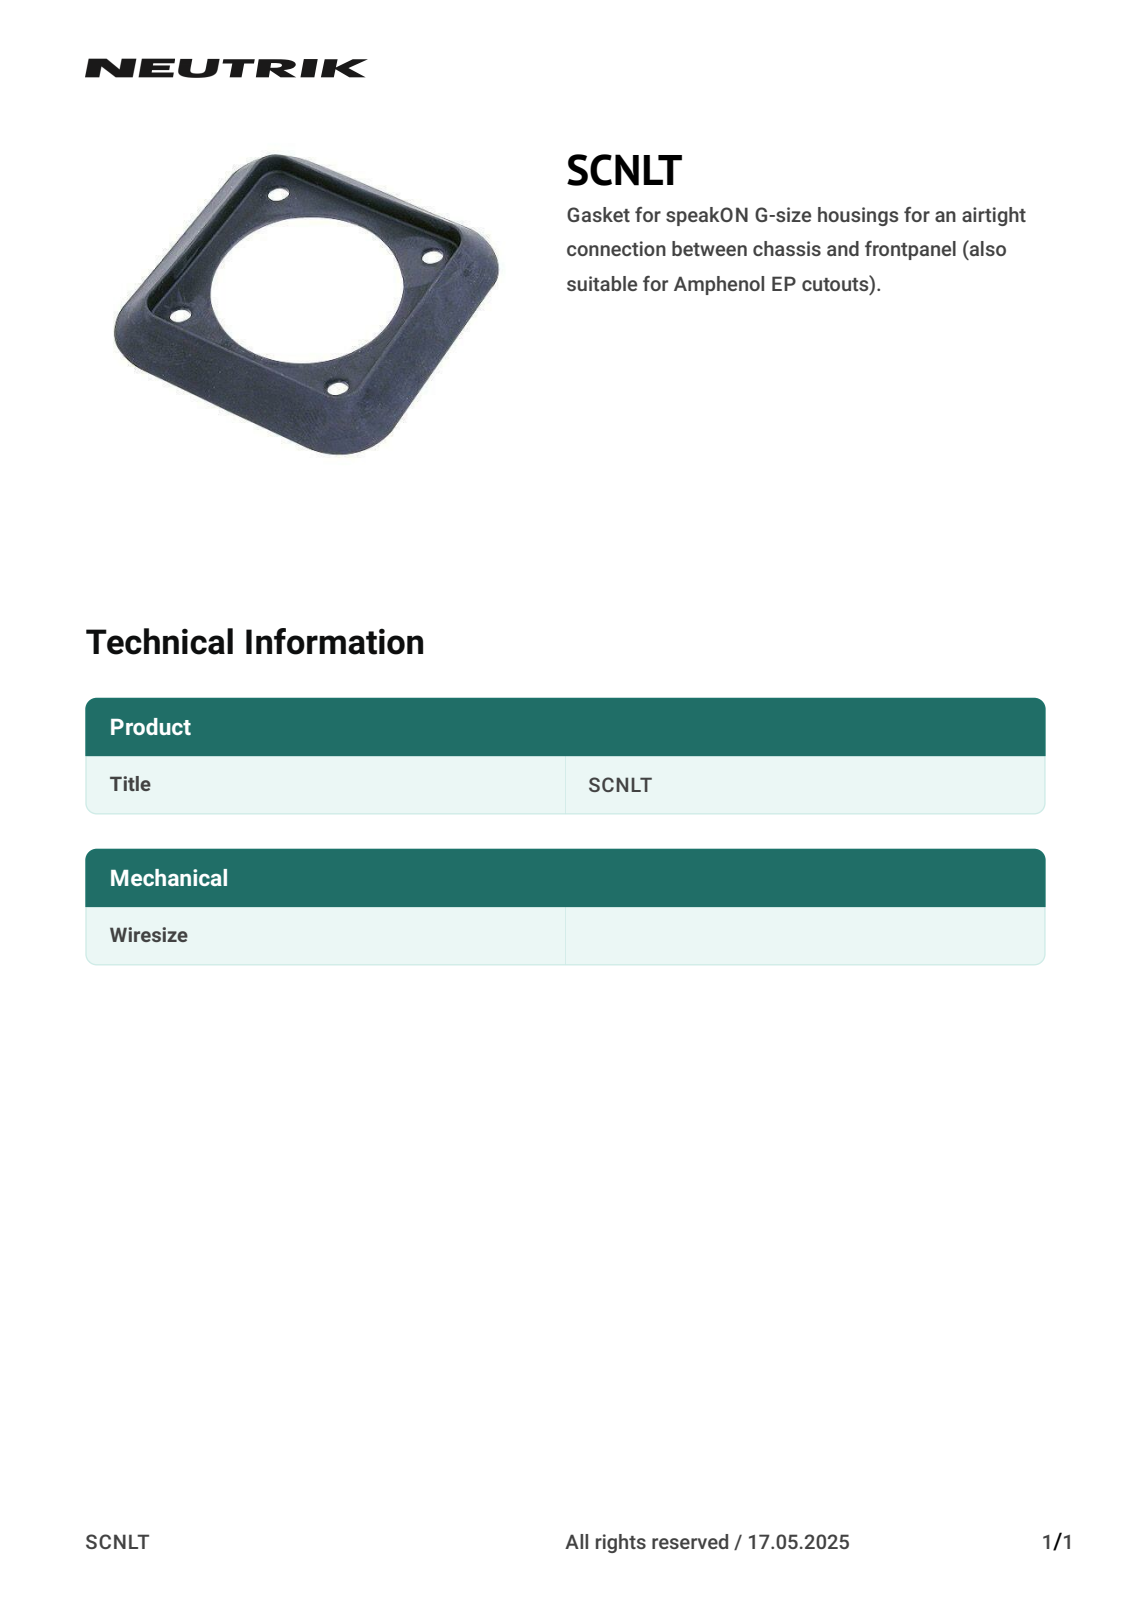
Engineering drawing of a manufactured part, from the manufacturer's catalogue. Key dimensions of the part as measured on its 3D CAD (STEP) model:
Part name (STEP PRODUCT): SCNLT
STEP written by: CREO PARAMETRIC BY PTC INC, 2018500 (CONFIG_CONTROL_DESIGN)
Units: millimetres
Bodies: 1 solid, 84 faces (18 planar, 34 cylindrical, 32 other)
Overall size (bounding box): 50 × 50 × 7
Volume: 3 131 mm³ · Surface area: 4 691 mm²
Round holes (diameter × count): ⌀3.5 ×4, ⌀31 ×1
Partial cylindrical surfaces — rounded edges, fillets, slot ends (radius × count): R0.5 ×8, R0.3 ×4, R0.4 ×4, R3.4 ×4, R5.29 ×4
Main face-to-face distances: 1, 38, 2
Hole centre spacings: 20.65, 29.2, 41.3
